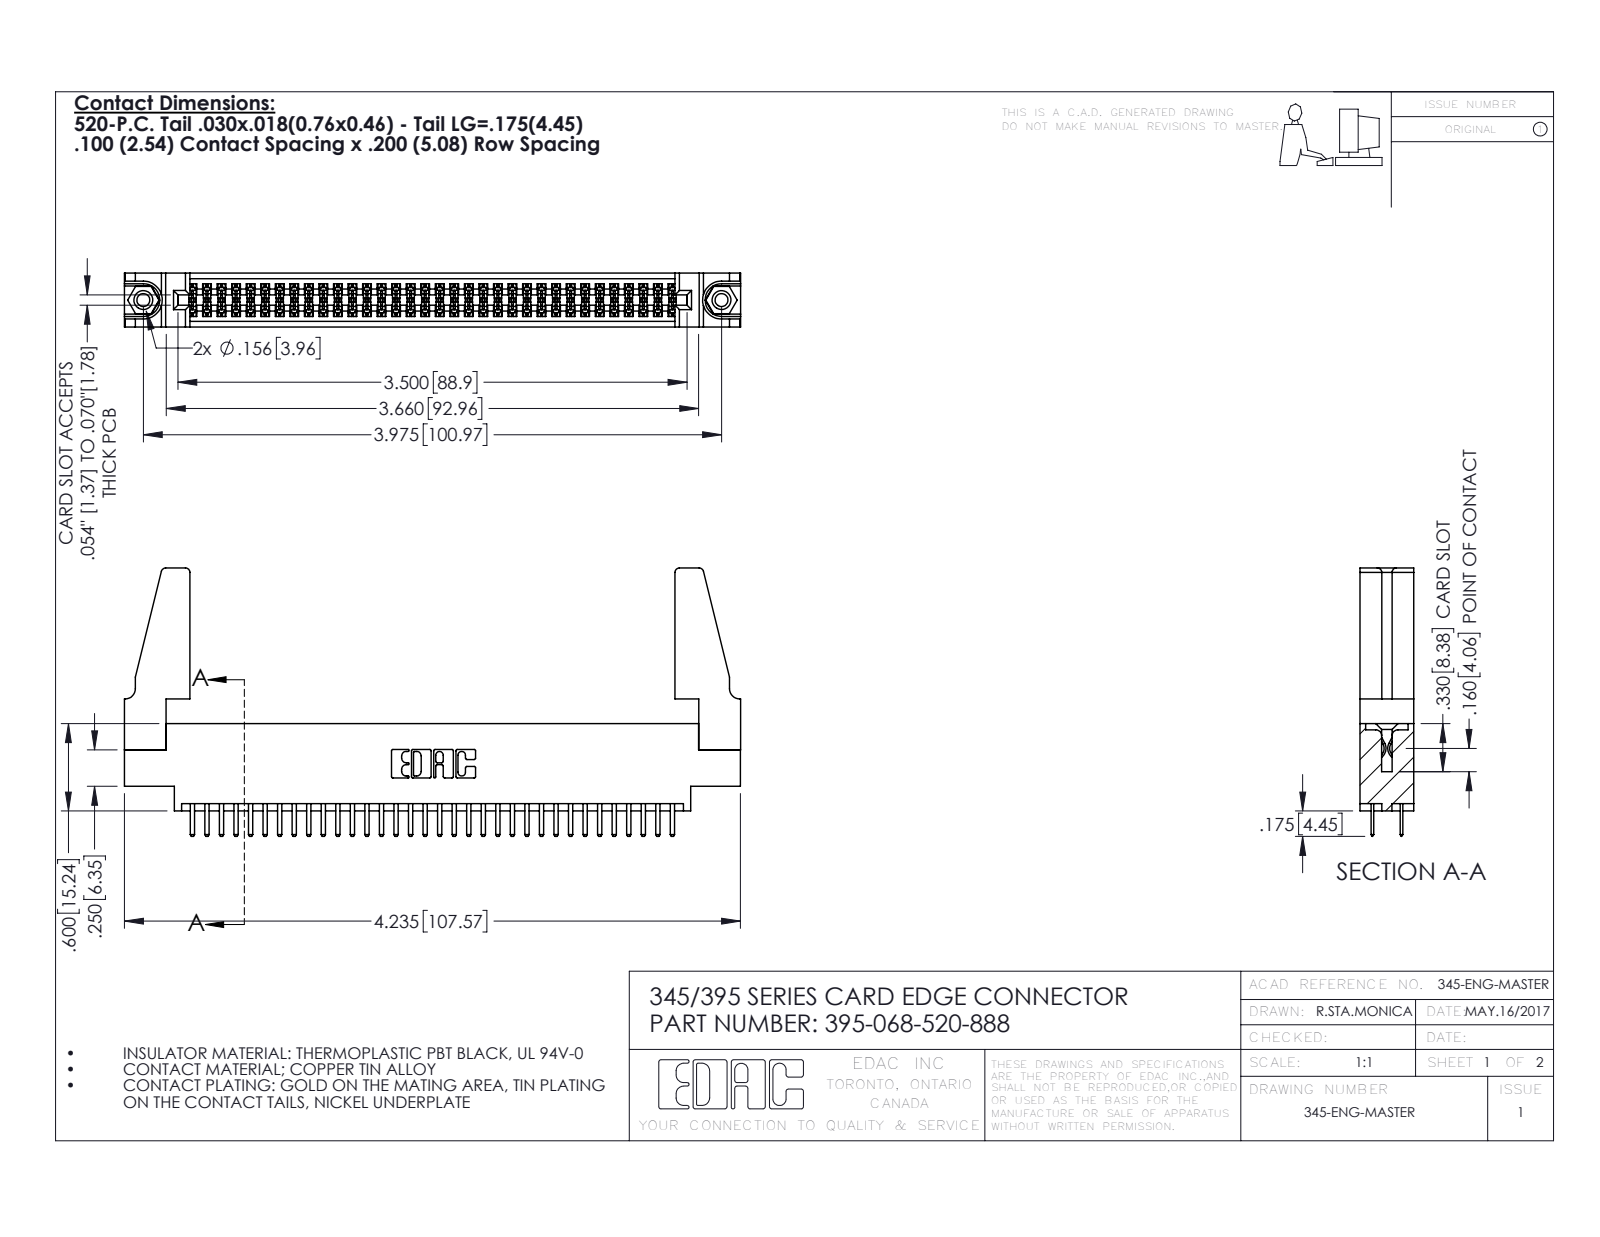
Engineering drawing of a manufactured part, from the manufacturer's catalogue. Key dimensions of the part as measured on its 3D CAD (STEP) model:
Part name (STEP PRODUCT): 345-250-001_345-250-001-102; 395-068-520-888; 345 Part_0.170 Offset - 0.156 Dia-TH; 345-220-078_345-220-088 (+1 more)
STEP written by: SolidWorks 2016 (CONFIG_CONTROL_DESIGN)
Units: inches
Bodies: 73 solids, 3926 faces (2536 planar, 1374 cylindrical, 16 other)
Overall size (bounding box): 4.236 × 1.845 × 0.37
Volume: 0.823 in³ · Surface area: 28.17 in²
Round holes (diameter × count): ⌀0.089 ×2, ⌀0.125 ×2, ⌀0.156 ×2, ⌀0.064 ×1
Round bosses / shafts (diameter × count): ⌀0.155 ×2
Partial cylindrical surfaces — rounded edges, fillets, slot ends (radius × count): R0.006 ×102, R0.01 ×72, R0.01 ×22, R0.03 ×8, R0.007 ×6, R0.031 ×6, R0.026 ×3, R0.014 ×2
Main face-to-face distances: 0.072, 0.37, 0.298, 0.2, 0.098, 0.272, 0.025, 0.225, 0.022, 0.175
Hole centre spacings: 0.27, 3.74, 3.975
